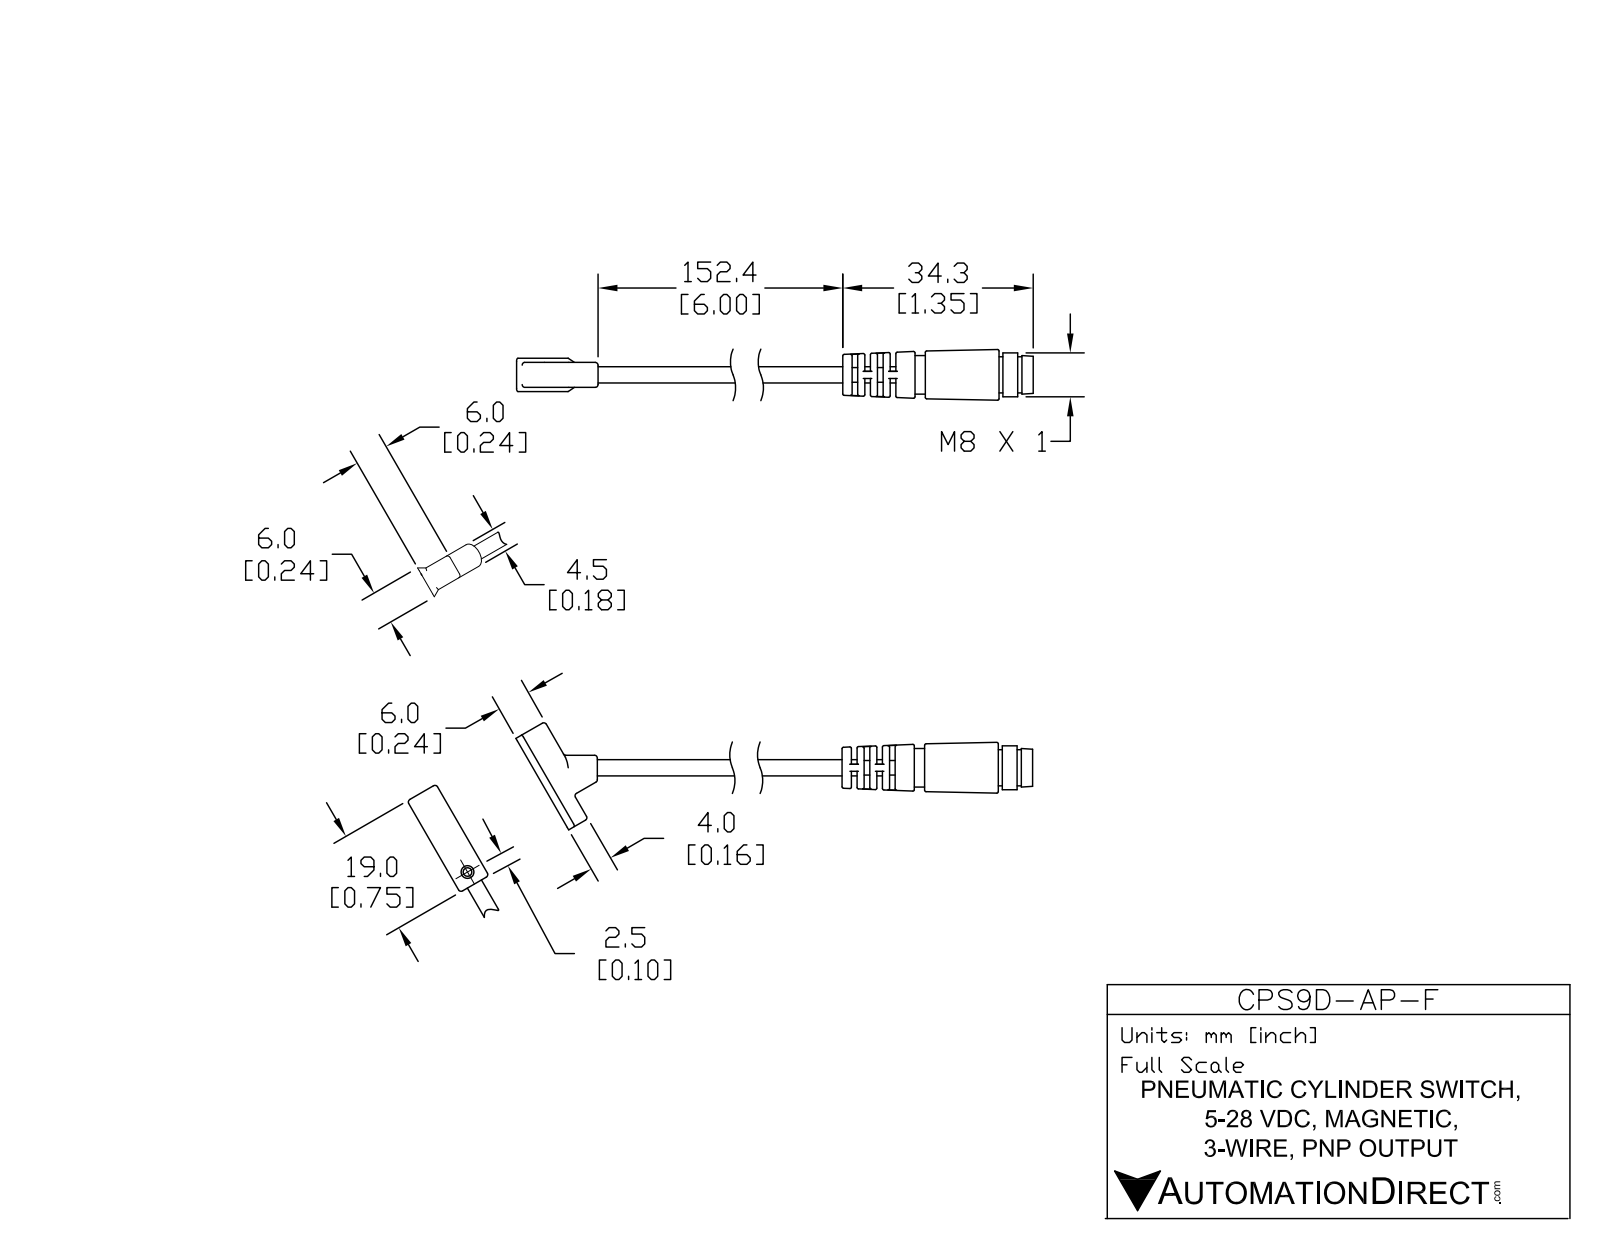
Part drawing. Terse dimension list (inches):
name: CPS9D-AP-F
written by: SolidWorks 2014 (AUTOMOTIVE_DESIGN)
unit: in
bodies: 1 solid, 171 faces (58 planar, 53 cylindrical, 60 other)
size: 5.683 × 3.597 × 0.36
volume: 0.178 in³; area: 4.666 in²
holes: 1× ⌀0.091, 1× ⌀0.227
bosses: 3× ⌀0.04, 1× ⌀0.311, 1× ⌀0.273, 1× ⌀0.256, 1× ⌀0.115
rounds: 20× R0.02, 1× R0.089
face distances: 0.09, 0.05, 0.04, 0.18, 0.177, 0.09, 0.13, 0.22, 0.27, 0.286
